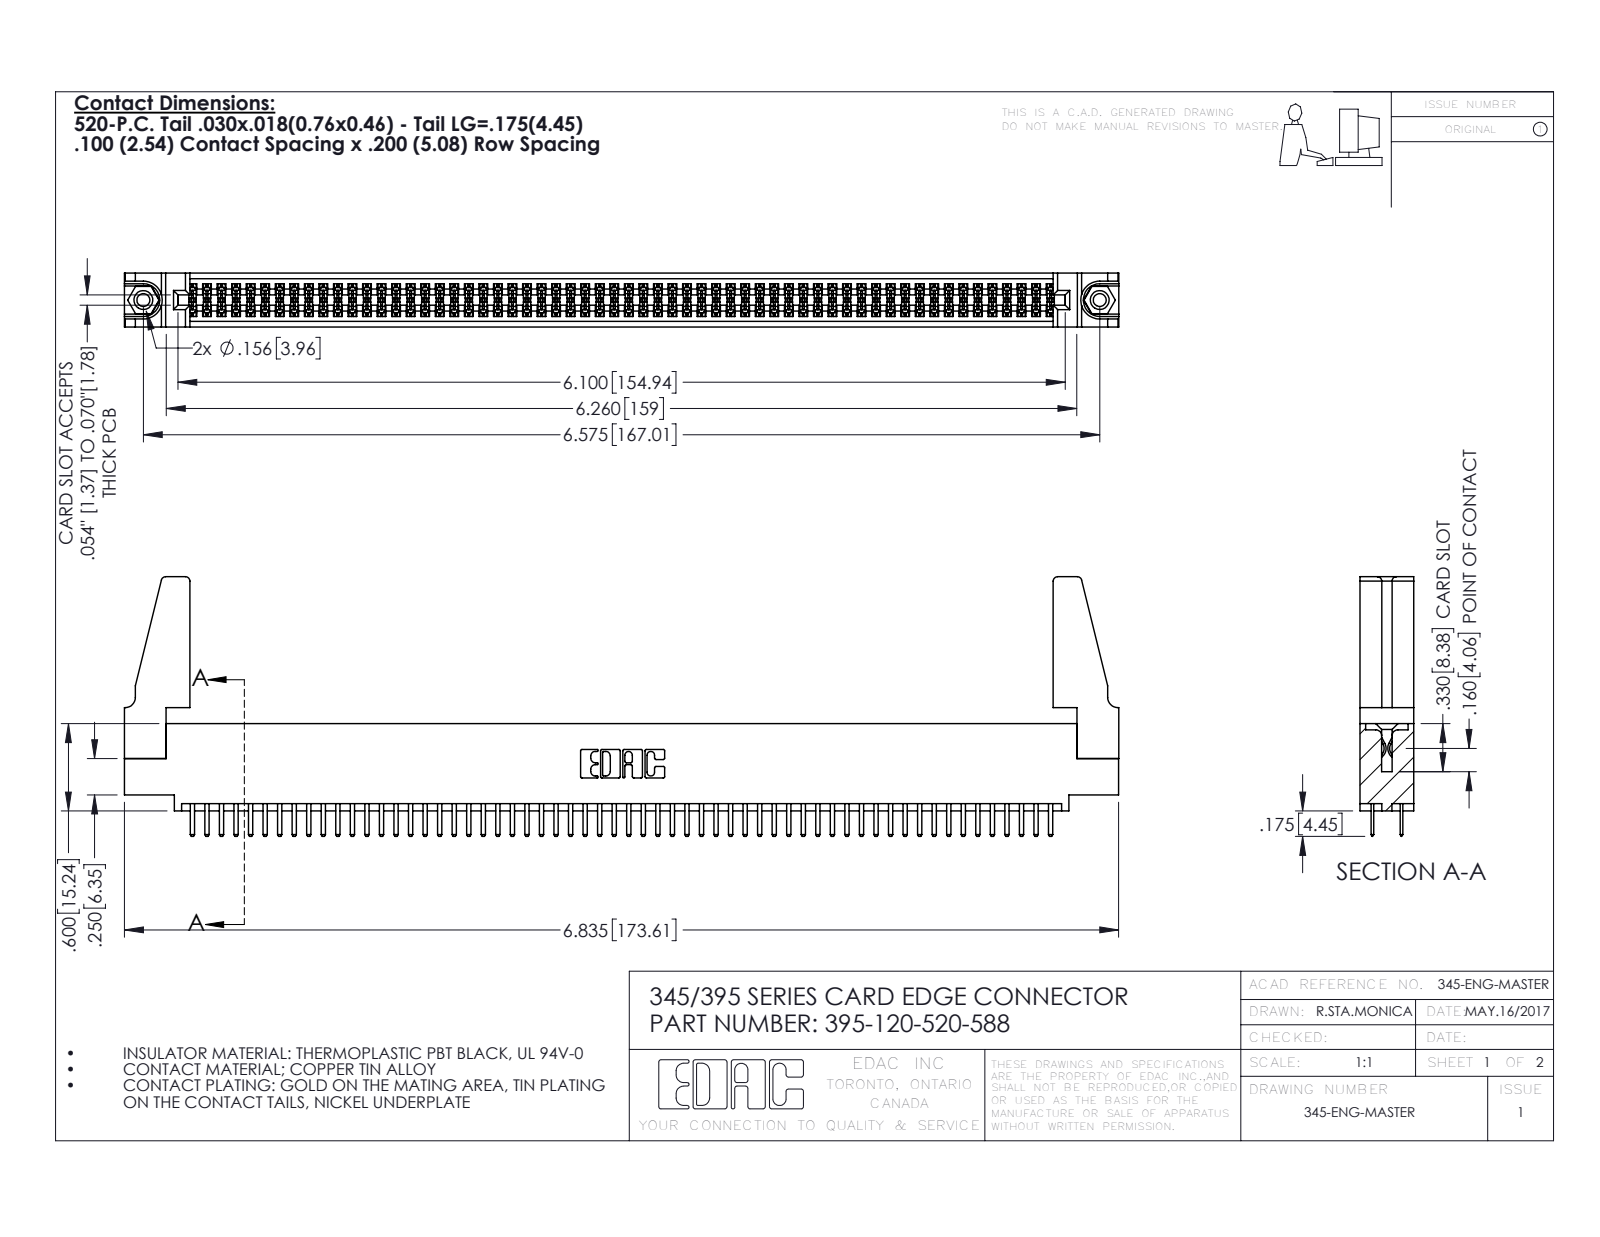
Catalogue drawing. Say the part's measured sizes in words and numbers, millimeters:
The part is named "345-250-001_345-250-001-102; 345-220-078_345-220-088; 395-120-520-588; 345-292-001_345-293-120 (+1 more)". Its 3-D file was written by "SolidWorks 2016 (CONFIG_CONTROL_DESIGN)". It is 125 solids with 6734 faces: 4356 planar, 2362 cylindrical and 16 other. Overall it measures 173.6 by 45.3 by 9.4 millimeters. Its volume is 20 160 cubic millimeters and its surface area 28 450 square millimeters. Round holes: 2 of diameter 2.3, 2 of diameter 3.2, 2 of diameter 4, 1 of diameter 1.6. Round bosses or shafts: 2 of diameter 3.9. Partial cylindrical surfaces (rounded edges, fillets, slot ends): 180 of radius 0.2, 124 of radius 0.3, 22 of radius 0.3, 8 of radius 0.8, 6 of radius 0.2, 6 of radius 0.8, 3 of radius 0.7, 2 of radius 0.4. The main face-to-face distances are 1.8, 7.6, 9.4, 5.1, 2.5, 6.9, 0.6, 5.7, 0.6, 1.8. The hole center spacings are 6.9, 161, 167.
